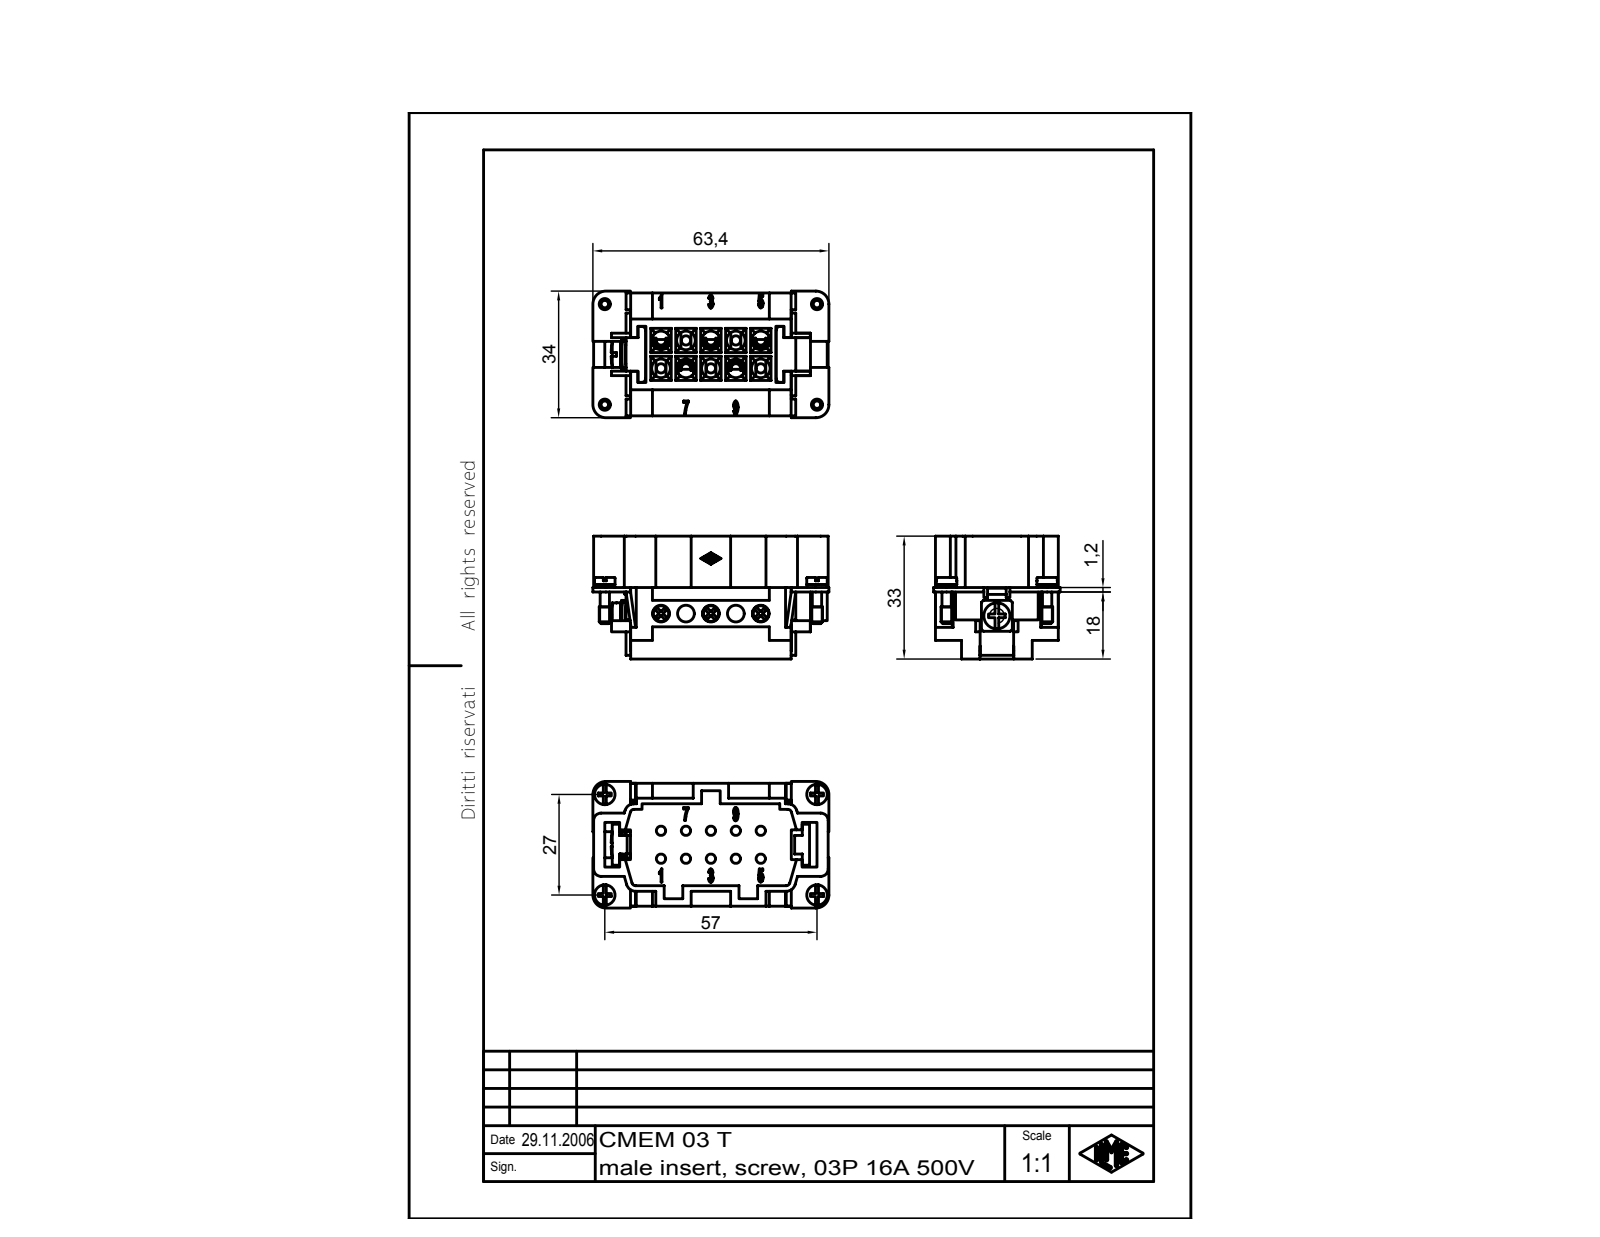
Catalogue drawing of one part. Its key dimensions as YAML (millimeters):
part_name: "CMEM_03_T"
step_written_by: "Creo Elements/Direct Modeling 18.1F 24-Jul-2014 (C) Parametric Technology GmbH (AUTOMOTIVE_DESIGN)"
units: millimeters
bodies: {solids: 1, faces: 1044, planar: 714, cylindrical: 220, other: 110}
overall_size: [63.4, 34, 33]
volume: 25571
surface_area: 21116
round_holes:
  - {diameter: 2.5, count: 10}
  - {diameter: 5, count: 10}
  - {diameter: 3, count: 5}
  - {diameter: 4.5, count: 5}
  - {diameter: 2.55, count: 4}
round_bosses_or_shafts:
  - {diameter: 5.5, count: 4}
  - {diameter: 5.3, count: 4}
  - {diameter: 3, count: 4}
  - {diameter: 2.5, count: 4}
  - {diameter: 7, count: 1}
partial_cylinders:
  - {radius: 0.1, count: 14}
  - {radius: 1, count: 8}
  - {radius: 2, count: 6}
  - {radius: 2.1, count: 5}
  - {radius: 2.5, count: 4}
  - {radius: 3.5, count: 4}
  - {radius: 5.5, count: 1}
face_to_face_distances: [1.5, 4, 3, 1, 5.5, 22, 26, 29, 20.5, 1.2]
hole_center_spacings: [6.7, 13.4, 10.06, 15.36, 20.1, 7.5, 17.97, 21.45]
